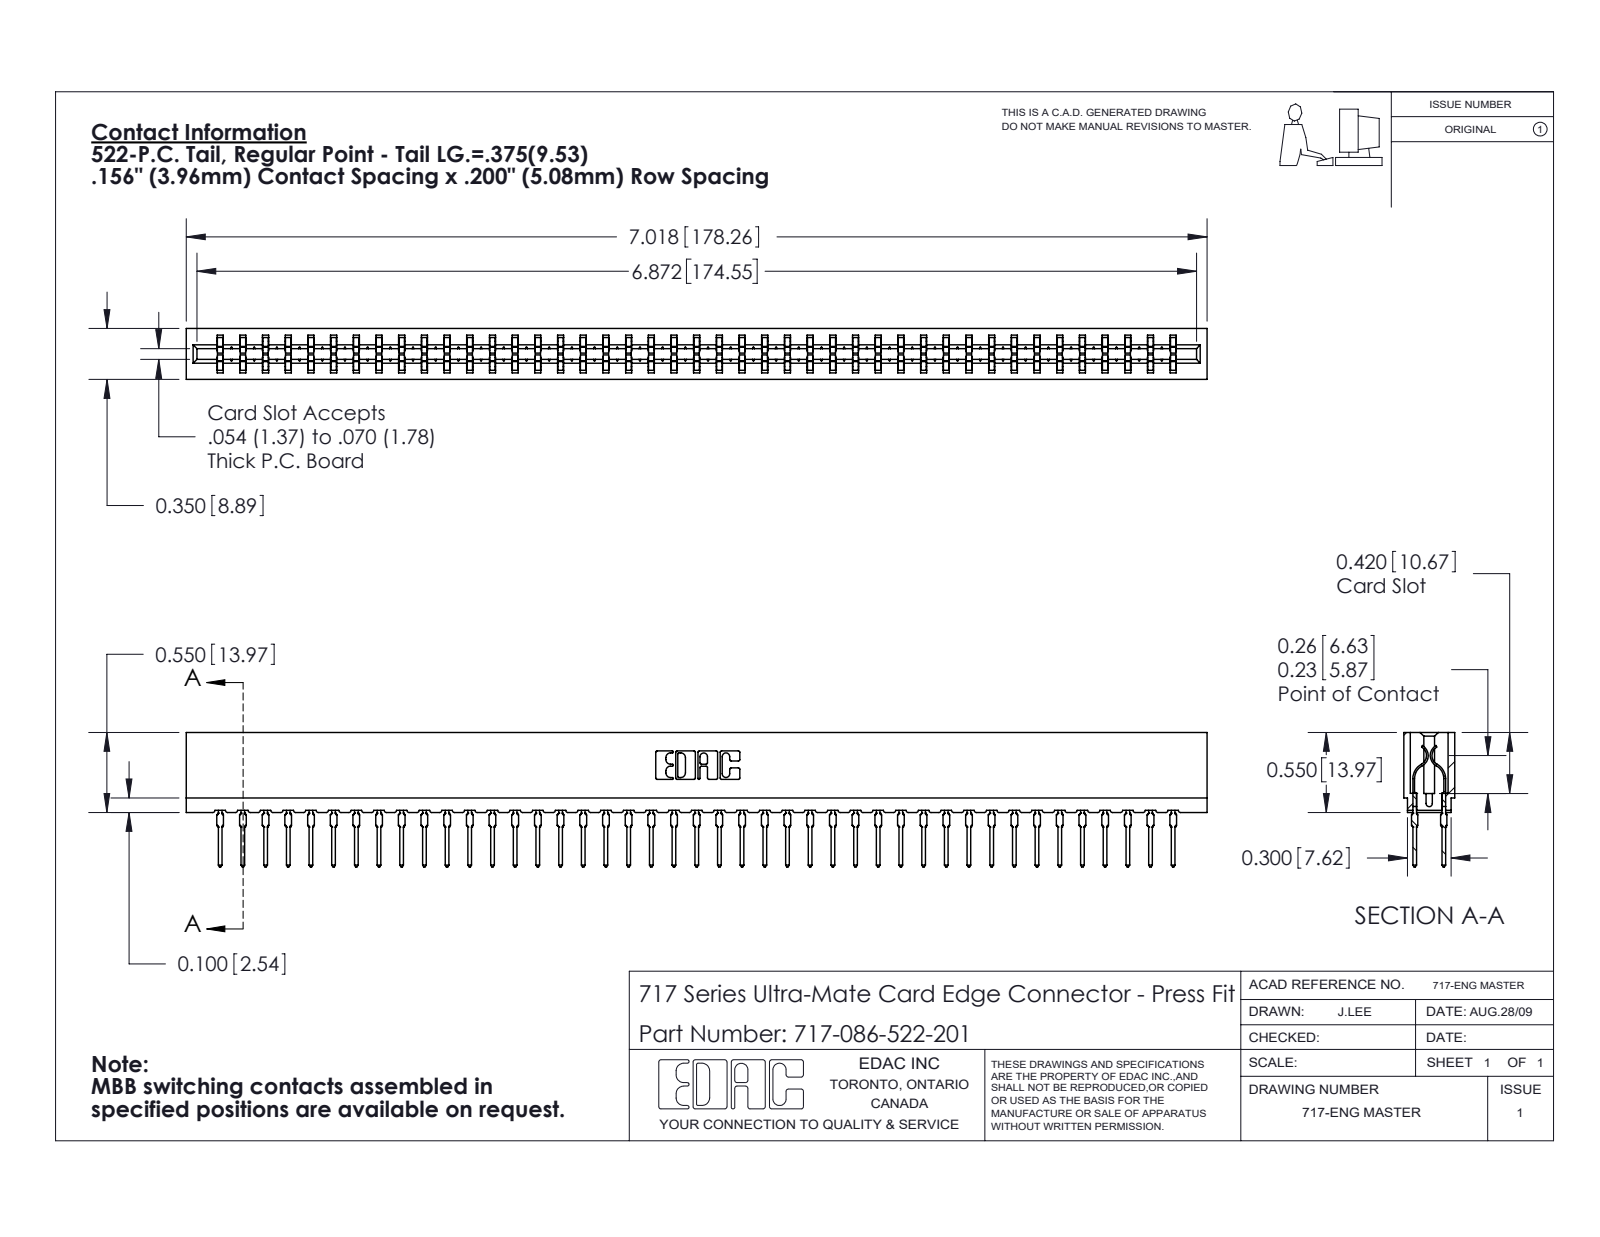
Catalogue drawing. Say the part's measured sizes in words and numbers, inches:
The part is named "717-086-522-201; 717 Part_Insulator Option - 06; 745-292-001_522". Its 3-D file was written by "SolidWorks 2020 (CONFIG_CONTROL_DESIGN)". It is 87 solids with 7834 faces: 4053 planar, 1545 cylindrical and 2236 other. Overall it measures 7.018 by 0.924 by 0.35 inches. Its volume is 0.948 cubic inches and its surface area 37.38 square inches. Partial cylindrical surfaces (rounded edges, fillets, slot ends): 172 of radius 0.021, 86 of radius 0.015, 22 of radius 0.01, 8 of radius 0.005, 8 of radius 0.011, 6 of radius 0.007, 6 of radius 0.031, 3 of radius 0.026. The main face-to-face distances are 0.212, 0.138, 0.35, 0.063, 0.287, 0.076, 0.149, 0.074, 0.045, 0.305.
